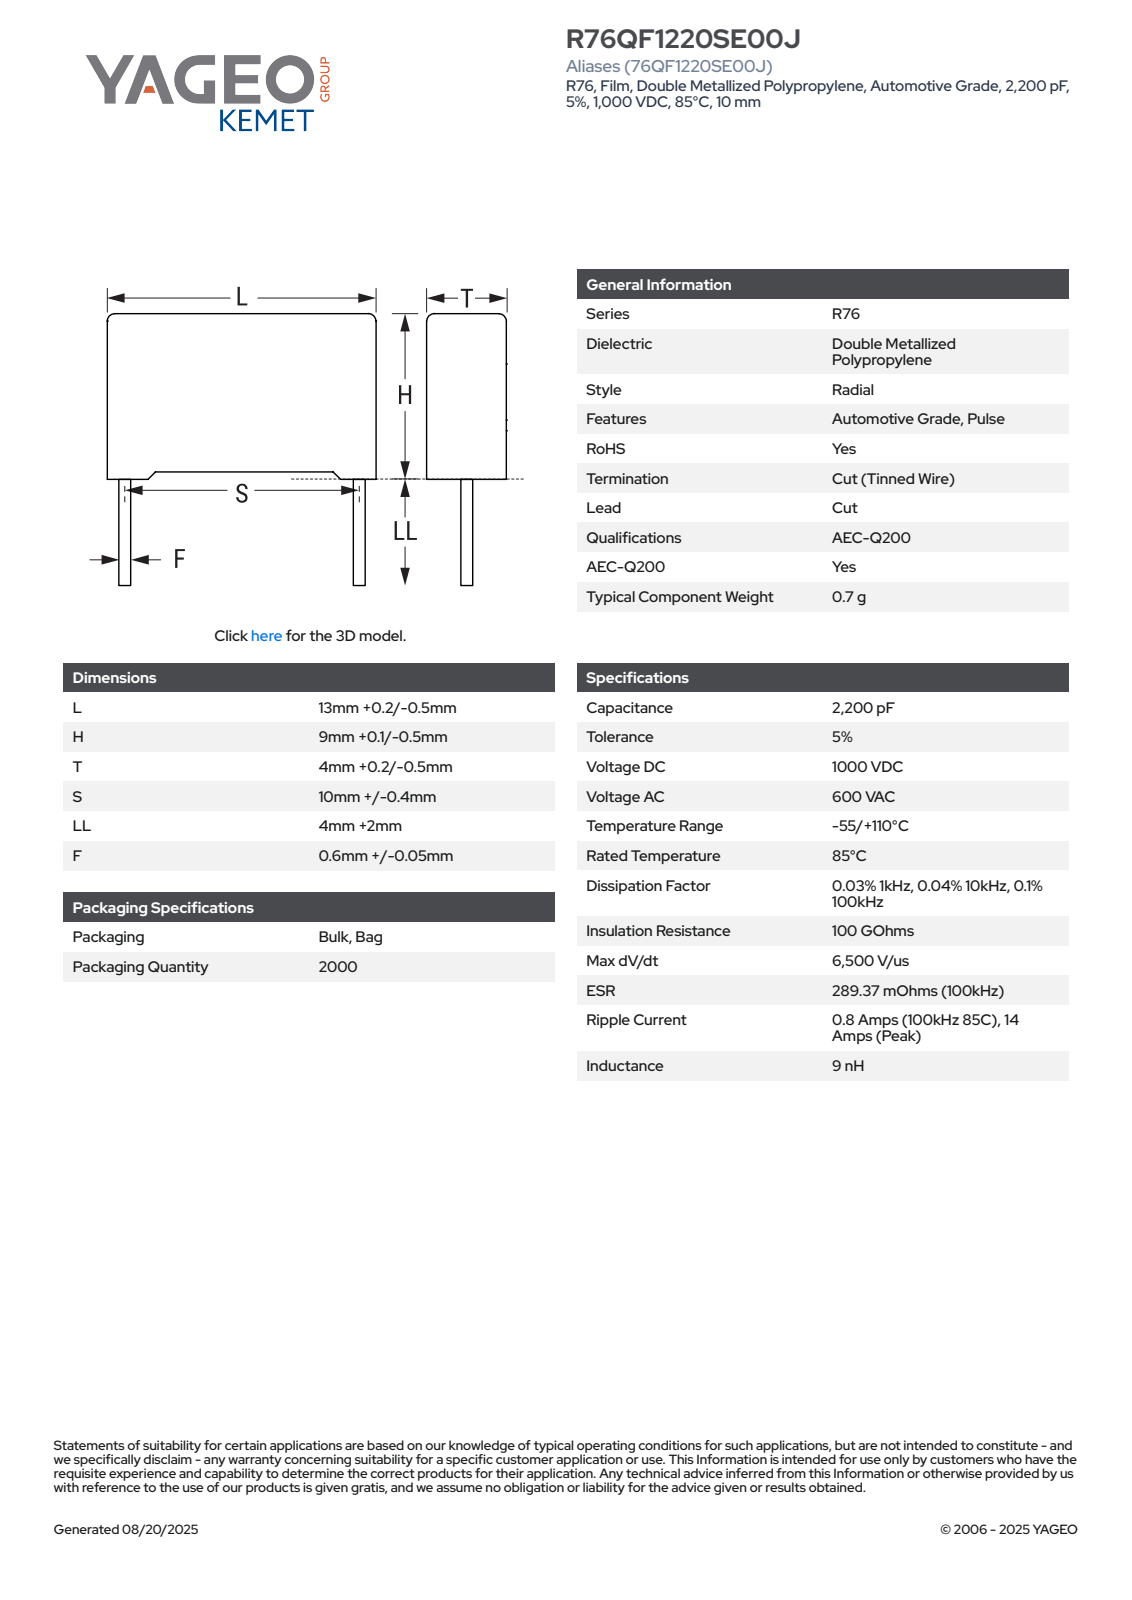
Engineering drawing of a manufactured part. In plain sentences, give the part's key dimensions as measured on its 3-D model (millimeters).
The part is named "CFR_RB2_13X9X4_L13.2H9.1T4.2S10LL6F0.65". Its 3-D file was written by "SolidWorks 2021 (AUTOMOTIVE_DESIGN)". It is 4 solids with 85 faces: 77 planar, 8 cylindrical and 0 other. Overall it measures 15.1 by 13.2 by 4.21 millimeters. Its volume is 475 cubic millimeters and its surface area 476 square millimeters. Round bosses or shafts: 2 of diameter 0.65. Partial cylindrical surfaces (rounded edges, fillets, slot ends): 4 of radius 0.5. The main face-to-face distances are 4.2, 8.35, 13.2, 0.44, 3.76, 0.75, 9.1, 3.32, 0.31, 8.79.
